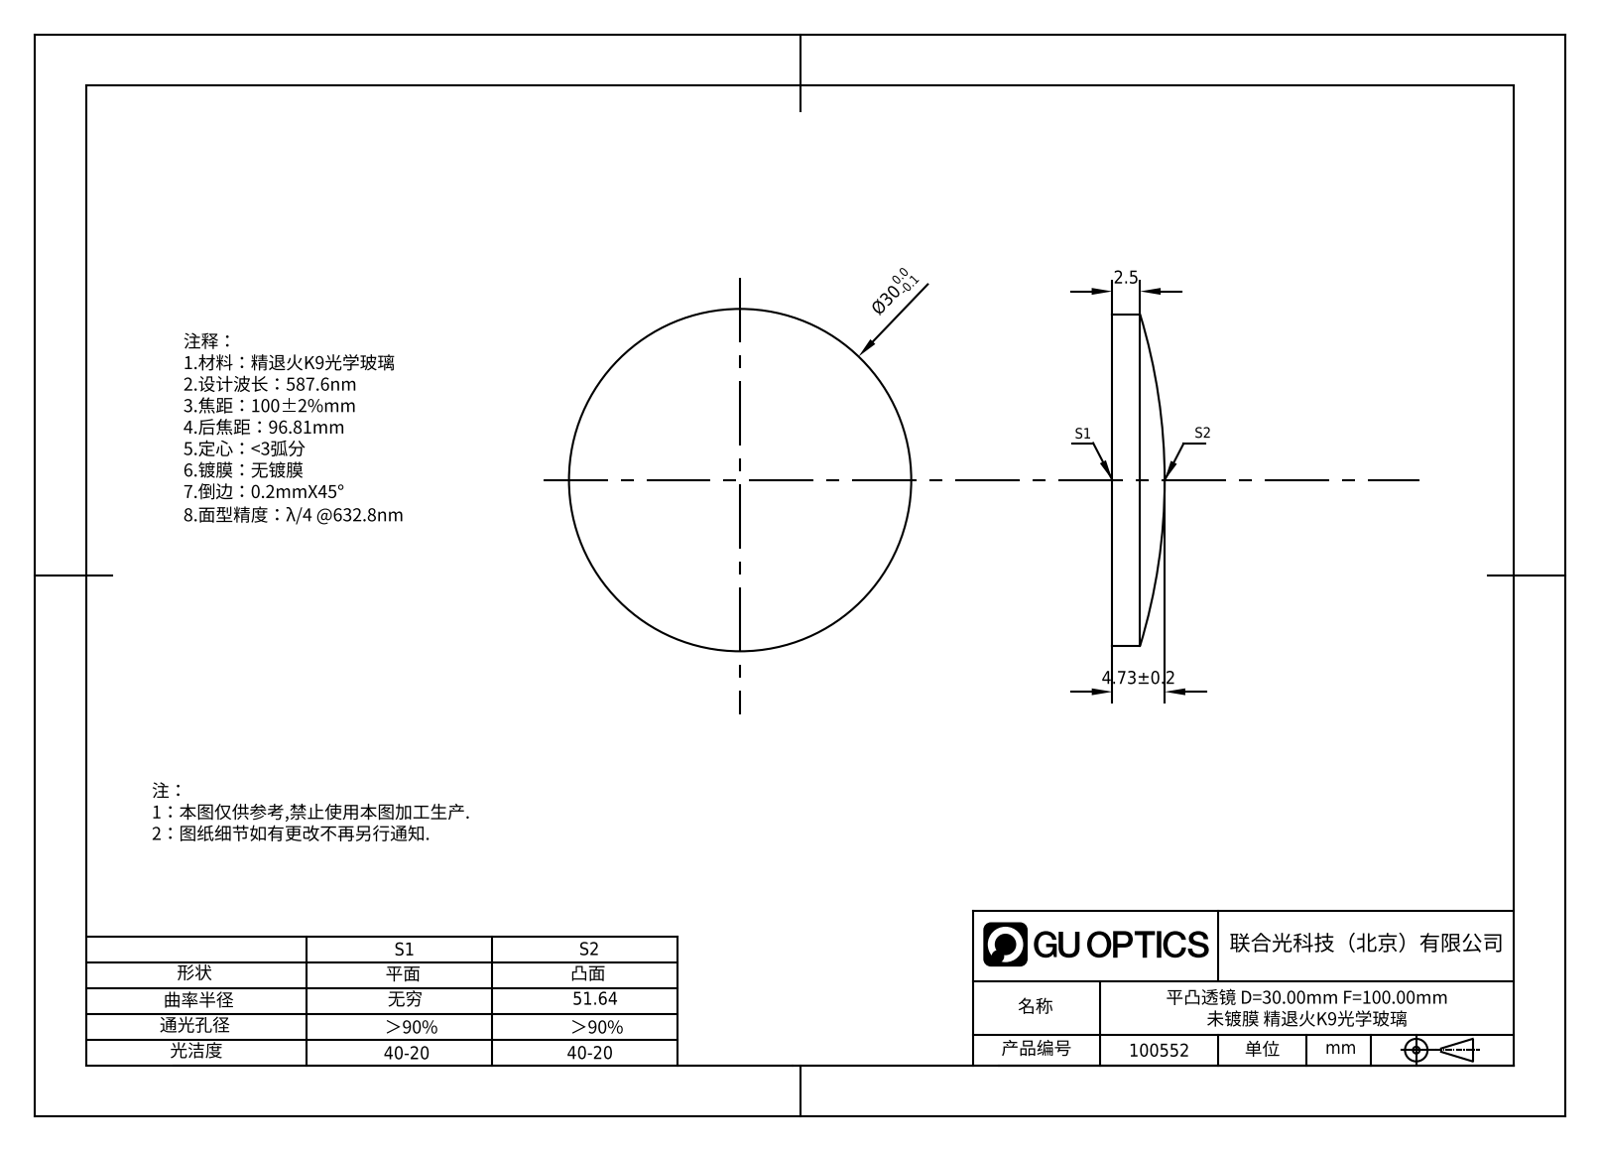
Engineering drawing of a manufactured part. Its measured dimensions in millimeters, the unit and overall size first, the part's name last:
Units: millimetres
Overall size (bounding box): 30 × 30 × 4.73
Round bosses / shafts (diameter × count): ⌀30 ×1
Volume: 2 561 mm³ · Surface area: 1 665 mm²
Bodies: 1 solid, 5 faces (1 planar, 2 cylindrical, 2 other)
Part name (STEP PRODUCT): 100552
STEP written by: SolidWorks 2020 (CONFIG_CONTROL_DESIGN)
